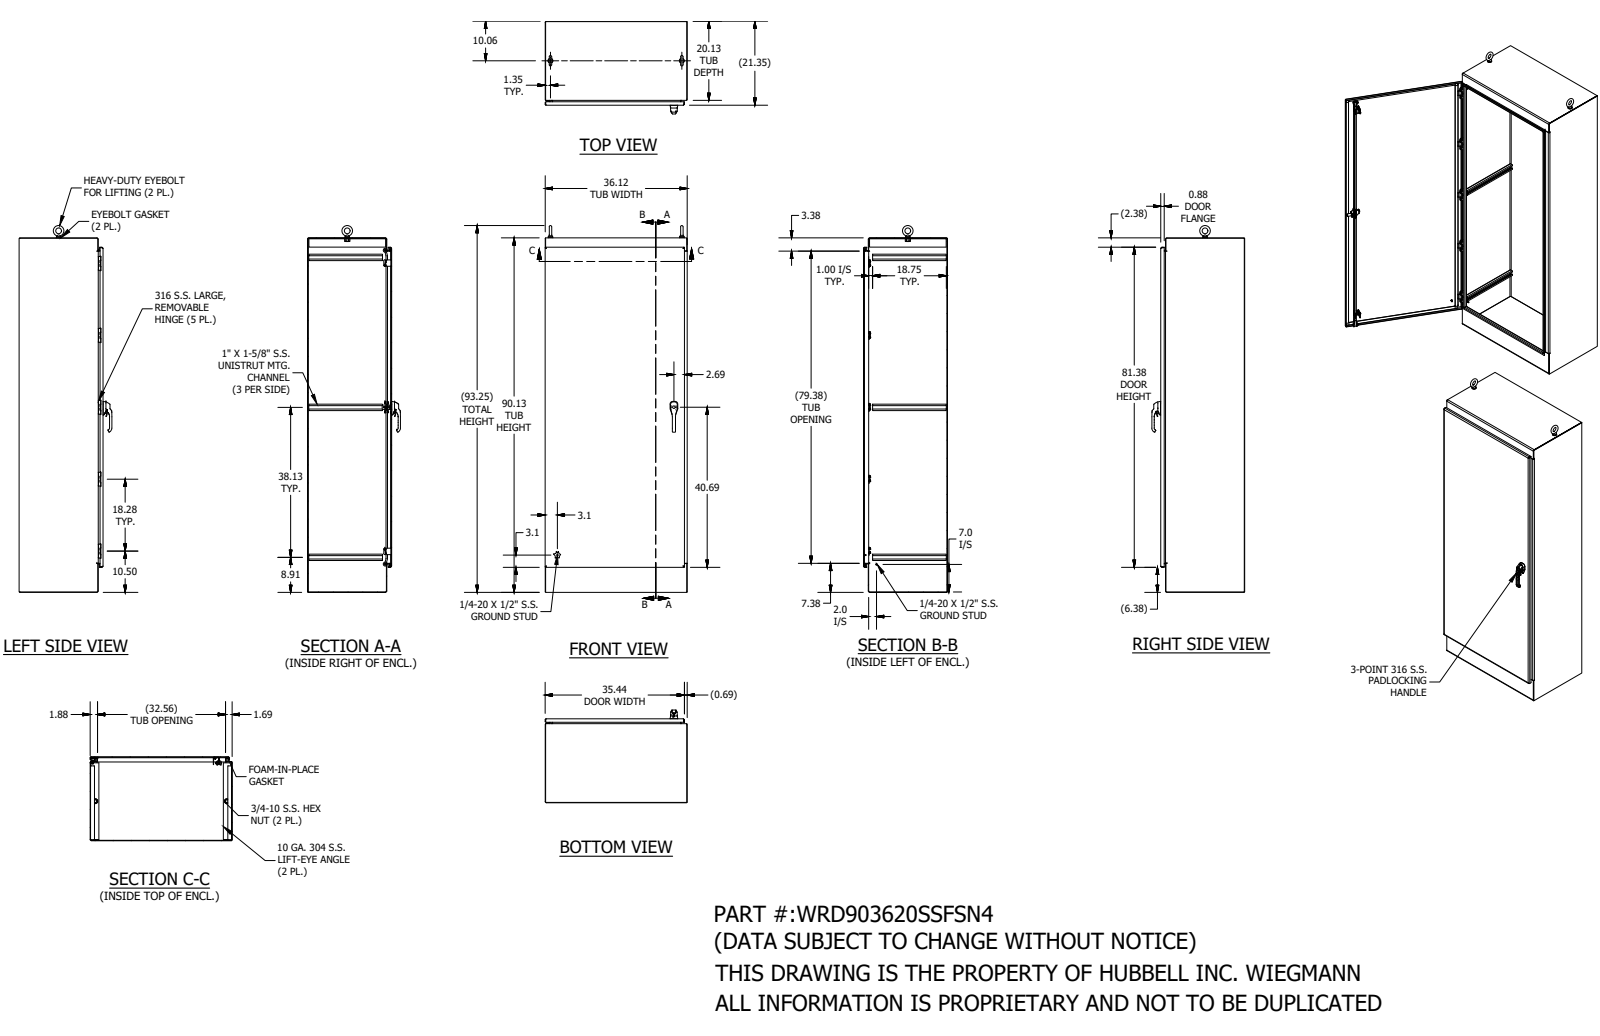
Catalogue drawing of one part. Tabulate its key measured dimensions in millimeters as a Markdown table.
| quantity | value |
| --- | --- |
| part name | WRD903620SSFSN4 |
| STEP written by | SolidWorks 2019 (AUTOMOTIVE_DESIGN) |
| units | millimeters |
| bodies | 112 solids, 4027 faces (1650 planar, 1411 cylindrical, 966 other) |
| overall size | 2368.5 × 917.7 × 599.4 |
| volume | 23 610 000 mm³ |
| surface area | 17 390 000 mm² |
| round holes (diameter × count) | 3.6 × 24, 5 × 10, 6.8 × 10, 7.5 × 10, 16.5 × 10, 6.7 × 8, 3.5 × 4, 4.2 × 4, 4.7 × 4, 5.1 × 4, 5.4 × 3, 7.1 × 3 |
| round bosses / shafts (diameter × count) | 15.9 × 10, 6.4 × 8, 6 × 4, 6 × 3, 31.8 × 2, 28.4 × 2, 25.4 × 2, 19.1 × 2 |
| partial cylindrical surfaces (radius × count) | 0.5 × 172, 0.3 × 114, 3.2 × 36, 1.6 × 22, 0.5 × 21, 1.6 × 16, 1.3 × 14, 2 × 14 |
| main face-to-face distances | 2.6, 914.9, 539.6, 537, 542.3, 539.6, 2.6, 912.3, 917.6, 2286.5 |
| hole center spacings | 0.5, 0.6, 25.4, 0.7, 9.7, 19.3, 464.3, 464.3 |
